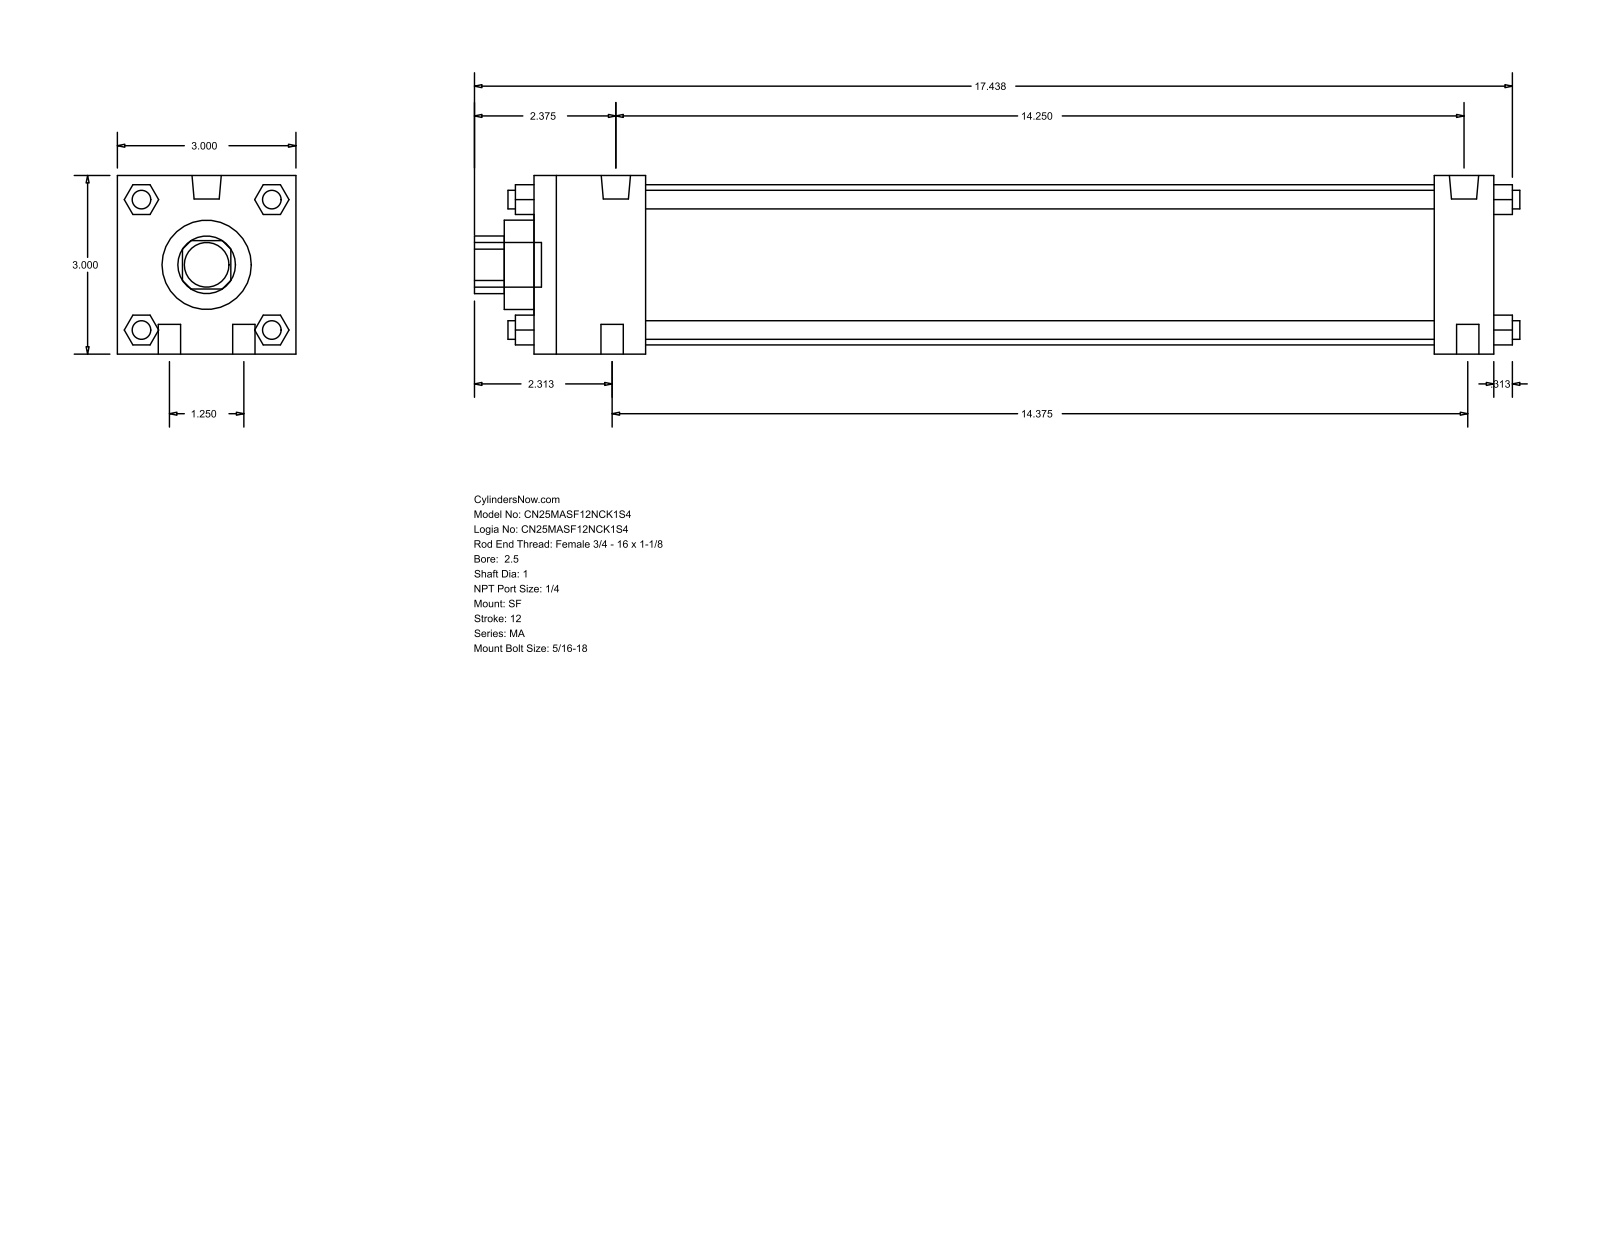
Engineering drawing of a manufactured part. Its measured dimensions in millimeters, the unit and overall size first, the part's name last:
Units: millimetres
Overall size (bounding box): 446.09 × 76.2 × 76.2
Round holes (diameter × count): ⌀25.4 ×1, ⌀38.1 ×1, ⌀68.33 ×1
Round bosses / shafts (diameter × count): ⌀7.94 ×6, ⌀9.53 ×4, ⌀12.49 ×2, ⌀19.05 ×1
Partial cylindrical surfaces — rounded edges, fillets, slot ends (radius × count): R12.29 ×1
Main face-to-face distances: 76.2, 409.58, 12.7, 384.17, 25.41, 47.63, 336.54, 361.95, 27.81, 48.17
Bodies: 0 solids, 124 faces (94 planar, 30 cylindrical, 0 other)
Part name (STEP PRODUCT): MA_SF__0250_1
STEP written by: GSSL Pune (CONFIG_CONTROL_DESIGN)
